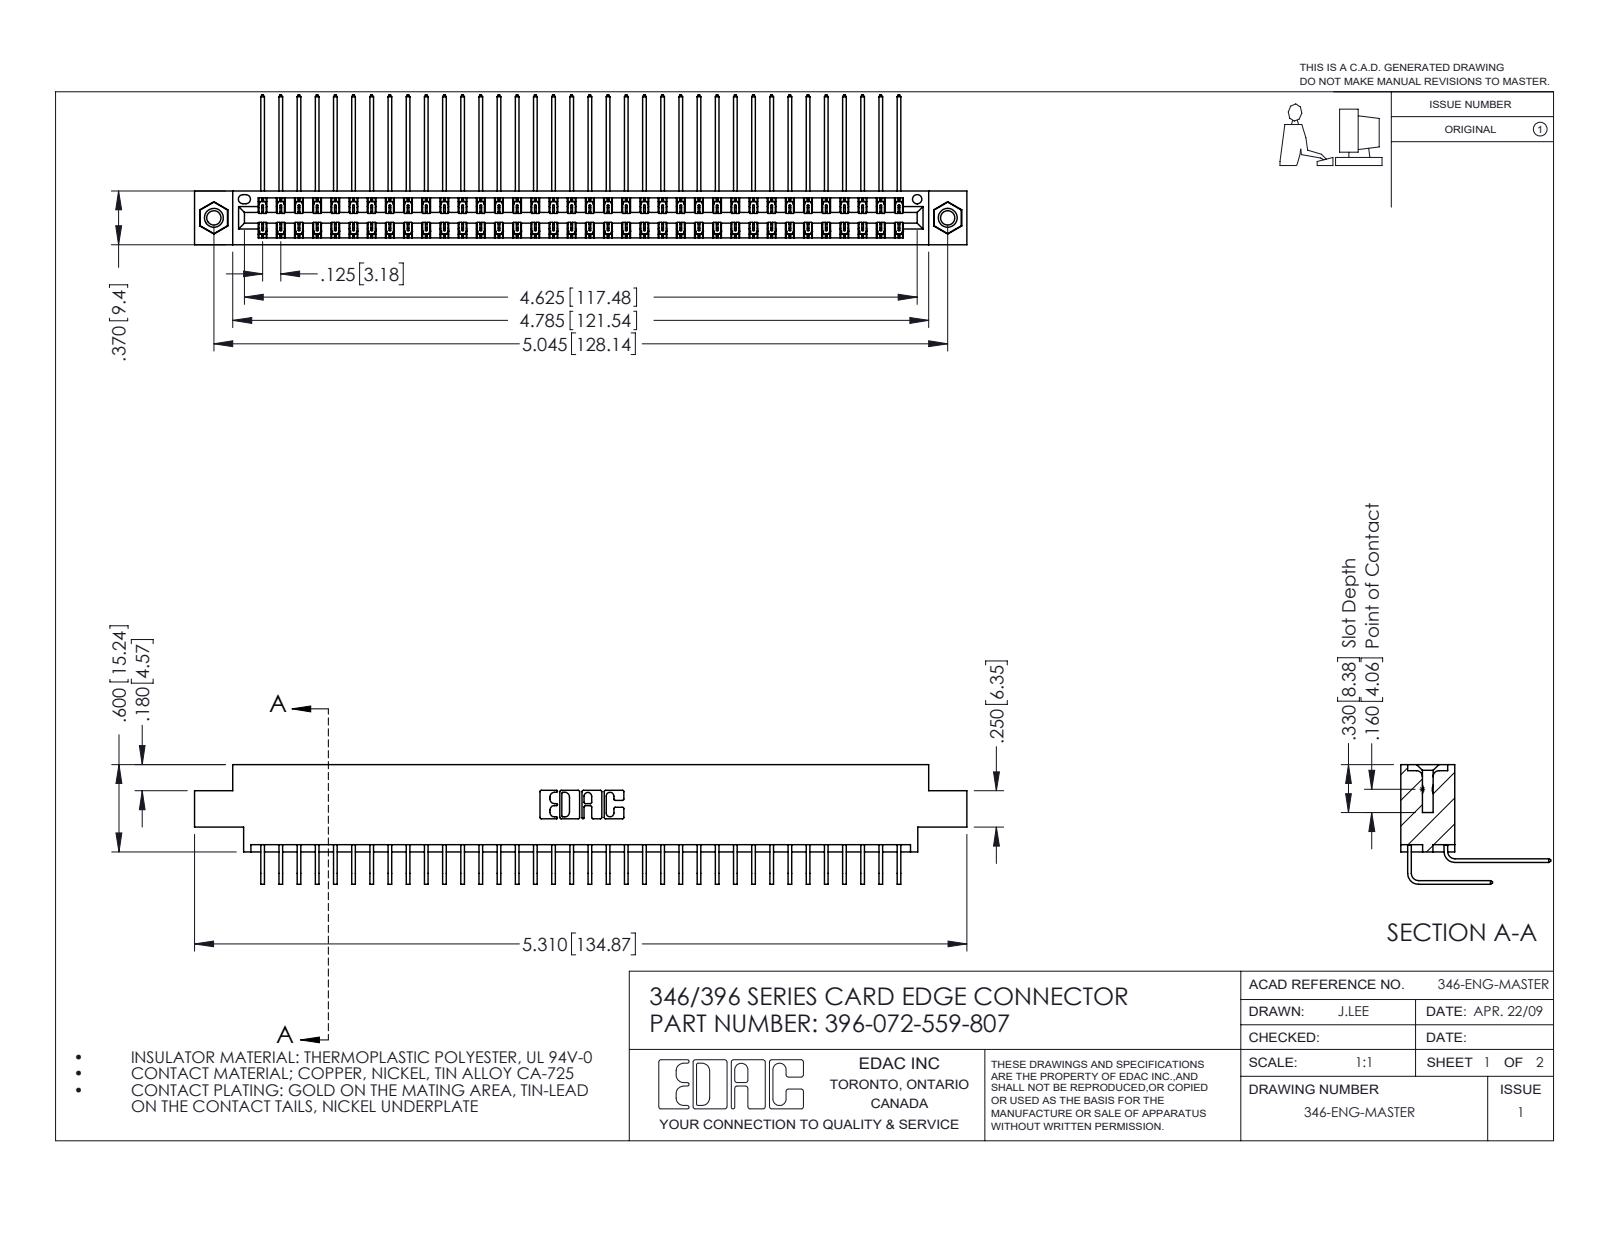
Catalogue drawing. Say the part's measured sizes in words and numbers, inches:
The part is named "396-072-559-807; 345-250-001_345-250-005-103; 346 Part_0.170 Offset - 0.156 Dia-TI; 345-292-001_559 Tail - 2 (+1 more)". Its 3-D file was written by "SolidWorks 2016 (CONFIG_CONTROL_DESIGN)". It is 75 solids with 4074 faces: 2776 planar, 1282 cylindrical and 16 other. Overall it measures 5.31 by 1.03 by 0.823 inches. Its volume is 0.815 cubic inches and its surface area 31.72 square inches. Round holes: 2 of diameter 0.098, 2 of diameter 0.125, 2 of diameter 0.156, 1 of diameter 0.064. Round bosses or shafts: 2 of diameter 0.155. Partial cylindrical surfaces (rounded edges, fillets, slot ends): 108 of radius 0.006, 22 of radius 0.01, 6 of radius 0.007, 6 of radius 0.031, 3 of radius 0.026, 2 of radius 0.014, 2 of radius 0.022, 2 of radius 0.024. The main face-to-face distances are 0.048, 0.322, 0.025, 0.37, 0.25, 0.072, 0.298, 0.275, 0.222, 0.148. The hole center spacings are 0.246, 4.836, 5.045.
